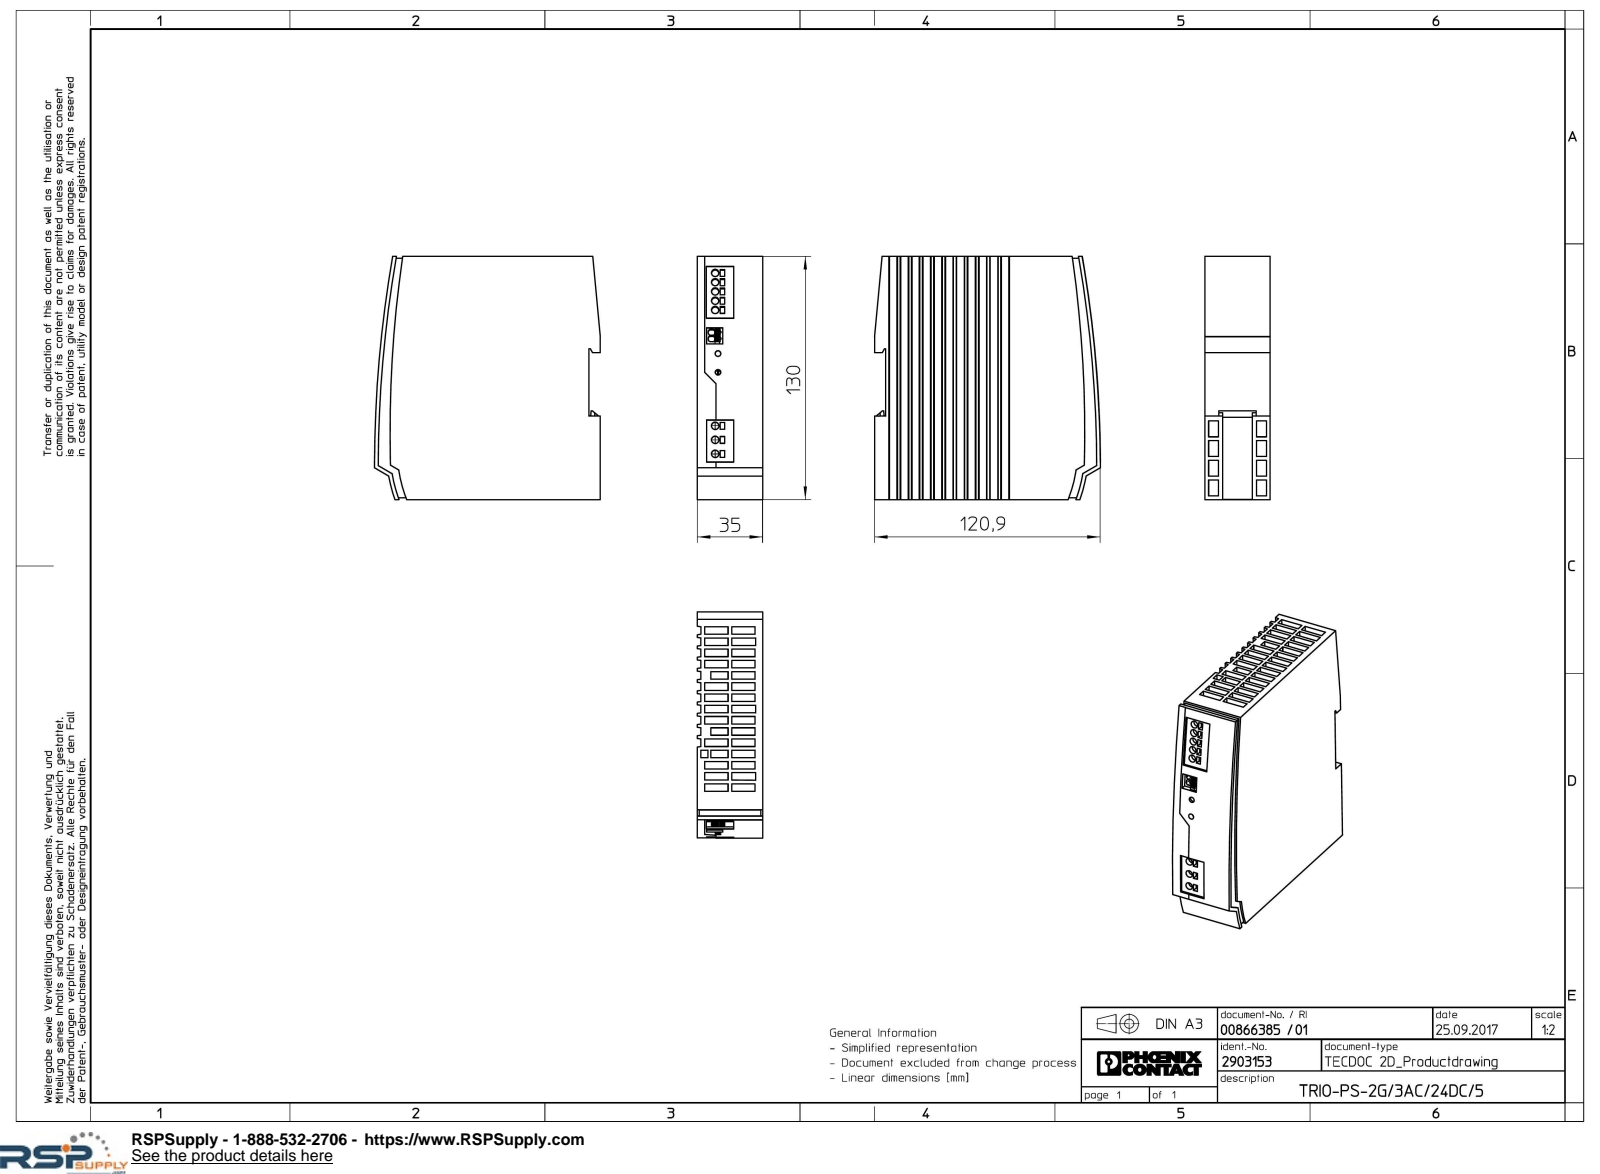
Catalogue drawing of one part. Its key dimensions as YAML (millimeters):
part_name: "TRIO_PS_2G_3AC_24DC_5-select"
step_written_by: "Creo Elements/Direct Modeling 18.1I 14-Aug-2016 (C) Parametric Technology GmbH (AUTOMOTIVE_DESIGN)"
units: millimeters
bodies: {solids: 1, faces: 622, planar: 583, cylindrical: 35, other: 4}
overall_size: [130, 121, 35]
volume: 497514
surface_area: 60376
round_holes:
  - {diameter: 4, count: 8}
  - {diameter: 3, count: 2}
partial_cylinders:
  - {radius: 0.57, count: 2}
  - {radius: 0.6, count: 2}
  - {radius: 1.03, count: 2}
  - {radius: 1.04, count: 2}
  - {radius: 69.15, count: 1}
  - {radius: 73, count: 1}
  - {radius: 75, count: 1}
  - {radius: 655.63, count: 1}
face_to_face_distances: [35, 2, 33, 3, 11.87, 17.8, 5.93, 29.67, 127, 1]
hole_center_spacings: [5, 10, 15, 7.49, 7.5, 14.99, 19.99]
